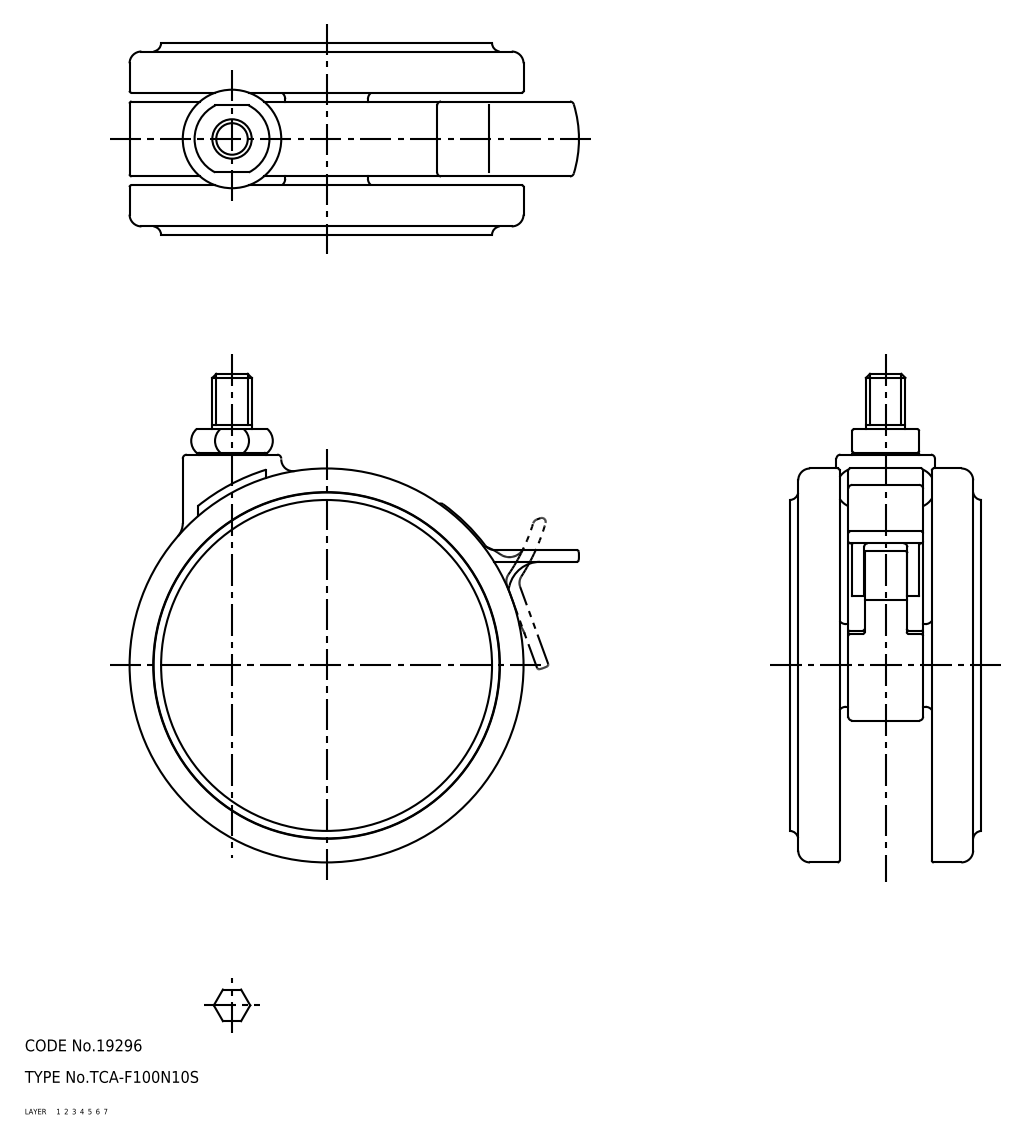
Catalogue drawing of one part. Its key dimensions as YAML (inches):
part_name: "TCA-F100N10S; caster"
step_written_by: "SolidWorks 2015 (AUTOMOTIVE_DESIGN)"
units: inches
bodies: {solids: 1, faces: 1520, planar: 528, cylindrical: 654, other: 338}
overall_size: [4.882, 4.491, 1.913]
volume: 11.29
surface_area: 148.2
round_holes:
  - {diameter: 0.094, count: 1}
  - {diameter: 0.118, count: 1}
  - {diameter: 0.13, count: 1}
  - {diameter: 0.142, count: 1}
  - {diameter: 0.228, count: 1}
  - {diameter: 0.24, count: 1}
  - {diameter: 0.318, count: 1}
  - {diameter: 0.354, count: 1}
  - {diameter: 0.366, count: 1}
  - {diameter: 0.421, count: 1}
  - {diameter: 0.484, count: 1}
  - {diameter: 0.512, count: 1}
round_bosses_or_shafts:
  - {diameter: 3.937, count: 1}
  - {diameter: 3.457, count: 1}
  - {diameter: 0.984, count: 1}
  - {diameter: 0.866, count: 1}
  - {diameter: 0.787, count: 1}
  - {diameter: 0.669, count: 1}
  - {diameter: 0.413, count: 1}
  - {diameter: 0.394, count: 1}
partial_cylinders:
  - {radius: 0.02, count: 63}
  - {radius: 0.039, count: 61}
  - {radius: 0.059, count: 21}
  - {radius: 0.008, count: 18}
  - {radius: 0.012, count: 17}
  - {radius: 0.079, count: 16}
  - {radius: 0.118, count: 7}
  - {radius: 0.028, count: 2}
face_to_face_distances: [0.071, 1.772, 1.843, 0.142, 1.701, 0.496, 1.276, 0.354, 1.417, 0.425]
hole_center_spacings: [0.843, 1.18, 1.732]
